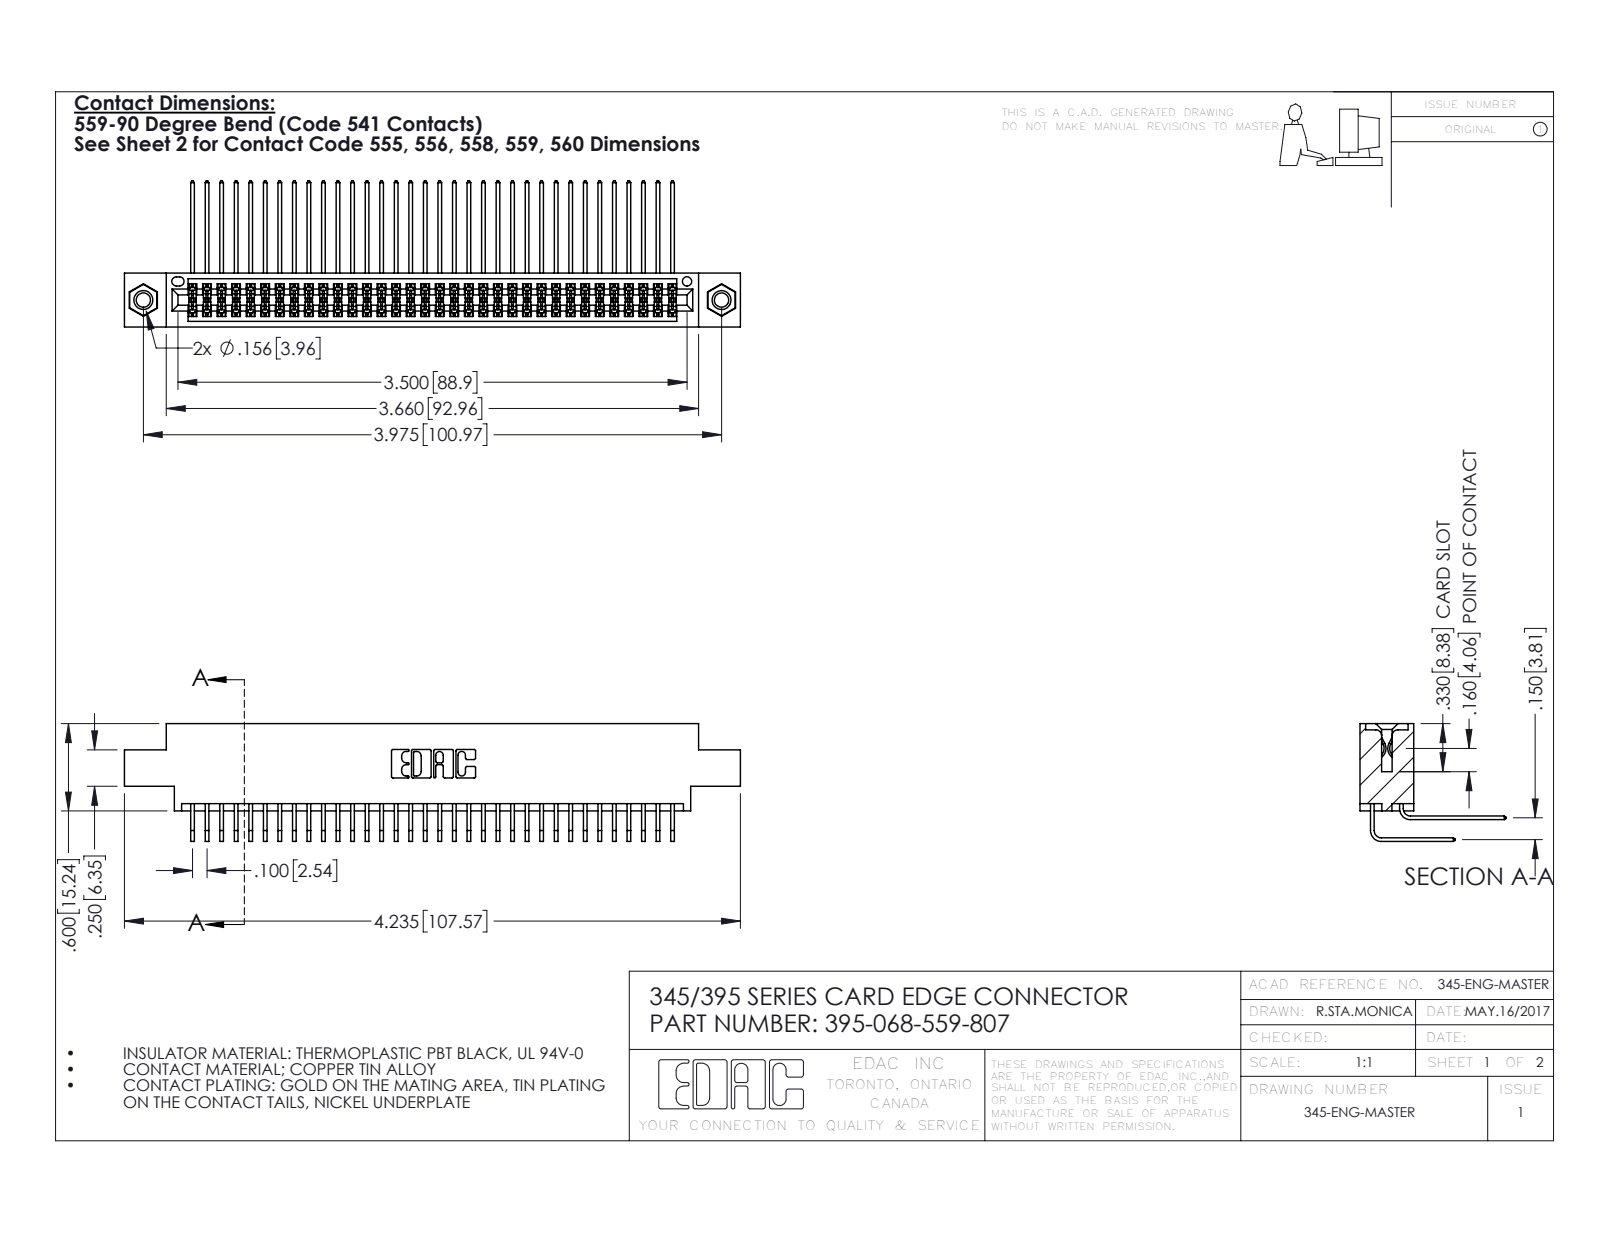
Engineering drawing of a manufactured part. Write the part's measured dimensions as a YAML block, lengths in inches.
part_name: "395-068-559-807; 345-292-001_558 559 Tail - 1; 345-250-001_345-250-005-103; 345 Part_0.170 Offset - 0.156 Dia-TI (+1 more)"
step_written_by: "SolidWorks 2016 (CONFIG_CONTROL_DESIGN)"
units: inches
bodies: {solids: 71, faces: 3726, planar: 2496, cylindrical: 1214, other: 16}
overall_size: [4.235, 1.005, 0.809]
volume: 0.649
surface_area: 27.26
round_holes:
  - {diameter: 0.098, count: 2}
  - {diameter: 0.125, count: 2}
  - {diameter: 0.156, count: 2}
  - {diameter: 0.064, count: 1}
round_bosses_or_shafts:
  - {diameter: 0.155, count: 2}
partial_cylinders:
  - {radius: 0.006, count: 103}
  - {radius: 0.01, count: 22}
  - {radius: 0.007, count: 6}
  - {radius: 0.031, count: 6}
  - {radius: 0.026, count: 3}
  - {radius: 0.014, count: 2}
  - {radius: 0.019, count: 2}
  - {radius: 0.022, count: 2}
face_to_face_distances: [0.072, 0.298, 0.37, 0.2, 0.098, 0.272, 0.025, 0.225, 0.175, 0.15]
hole_center_spacings: [0.27, 3.74, 3.975]
